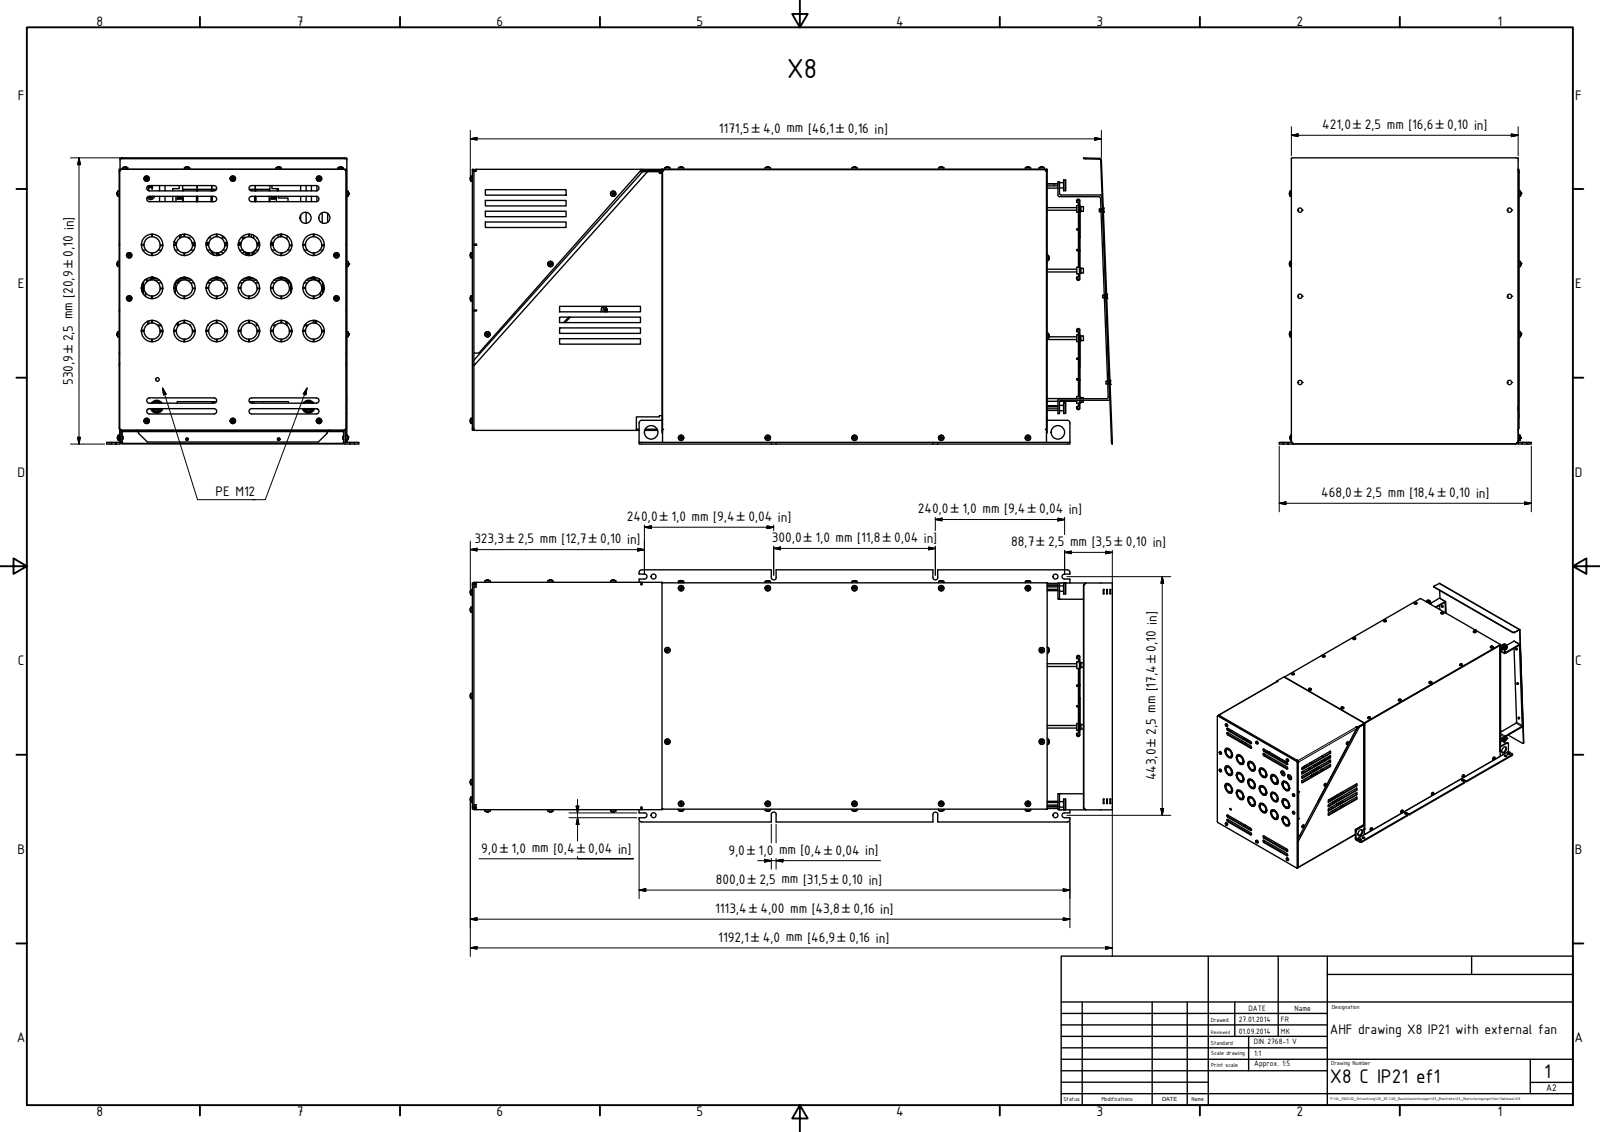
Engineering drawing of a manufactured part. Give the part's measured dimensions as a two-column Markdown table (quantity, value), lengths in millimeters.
| quantity | value |
| --- | --- |
| part name | 10100531 Seitenwand X8-A1; 10100530 Lüfterblech X8-A1; 10100529 Anschlussblech X8-A1; 10100404 Deckel X7-X8 (+8 more) |
| STEP written by | Autodesk Inventor 2015 (AUTOMOTIVE_DESIGN) |
| units | millimeters |
| bodies | 186 solids, 11900 faces (7341 planar, 2660 cylindrical, 1899 other) |
| overall size | 1192.06 × 530.87 × 468 |
| volume | 8 994 000 mm³ |
| surface area | 7 729 000 mm² |
| round holes (diameter × count) | 4.13 × 49, 6.5 × 47, 7 × 28, 4 × 21, 3.24 × 20, 40 × 18, 6 × 14, 5 × 10, 9 × 6, 10 × 6, 14 × 6, 3.95 × 4 |
| round bosses / shafts (diameter × count) | 5 × 51, 4.6 × 44, 1.4 × 16, 16 × 14, 30 × 12, 26.7 × 12, 8.5 × 10, 10 × 8 |
| partial cylindrical surfaces (radius × count) | 0.83 × 152, 1 × 135, 0.15 × 113, 0.5 × 71, 2 × 71, 3.25 × 65, 0.31 × 64, 0.1 × 61 |
| main face-to-face distances | 1, 2, 419, 420, 418, 3, 714, 421, 482.5, 1.5 |
| hole center spacings | 100, 21, 161, 389, 7.5, 200, 322, 400 |
